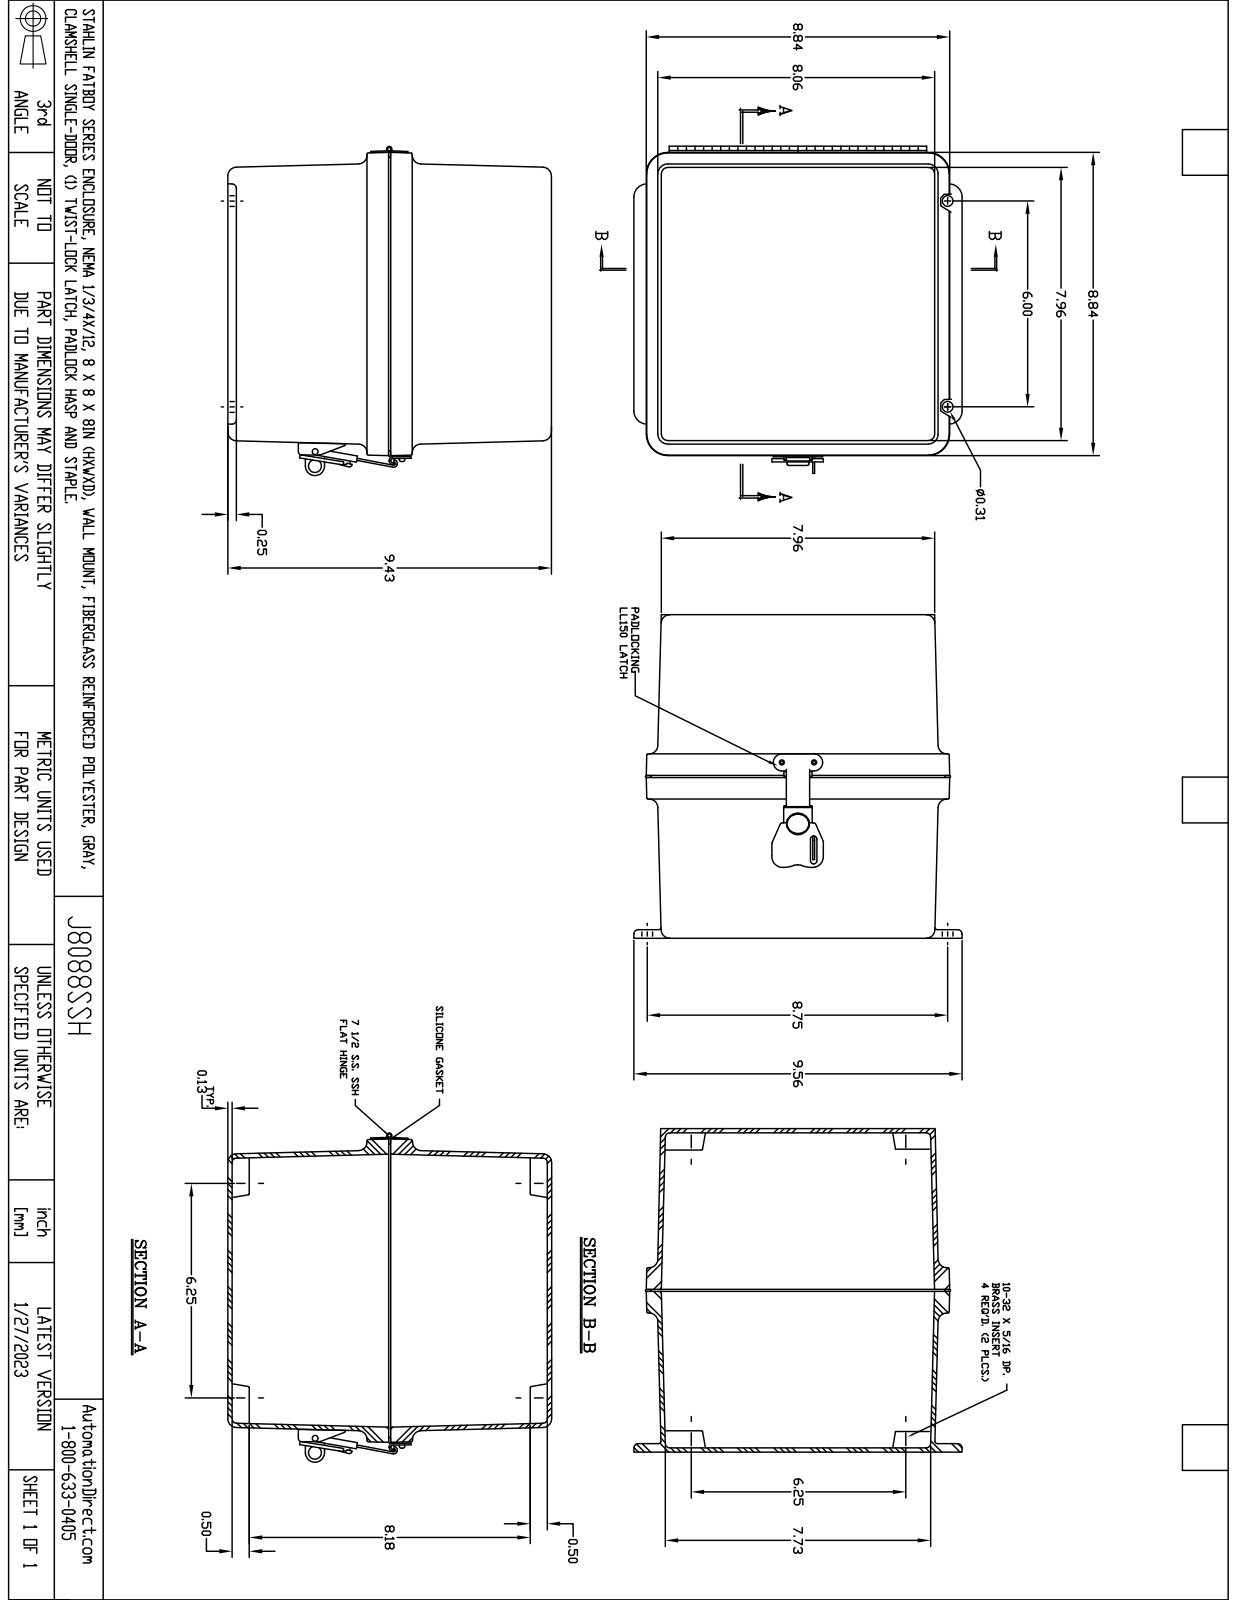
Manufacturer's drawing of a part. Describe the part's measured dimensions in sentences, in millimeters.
The part is named "M8088SSH". Its 3-D file was written by "SolidWorks 2018 (AUTOMOTIVE_DESIGN)". It is 35 solids with 1137 faces: 399 planar, 443 cylindrical and 295 other. Overall it measures 242.9 by 242.7 by 239.5 millimeters. Its volume is 1 172 000 cubic millimeters and its surface area 619 100 square millimeters. Round holes: 11 of diameter 3.9, 10 of diameter 3.6, 7 of diameter 4, 6 of diameter 3.5, 4 of diameter 5.5, 2 of diameter 3.3, 2 of diameter 4.2, 2 of diameter 5, 1 of diameter 2.2, 1 of diameter 2.7, 1 of diameter 3, 1 of diameter 3.5. Round bosses or shafts: 10 of diameter 6.4, 7 of diameter 6.9, 6 of diameter 3.2, 4 of diameter 3.2, 1 of diameter 14.8, 1 of diameter 13.3, 1 of diameter 5.3, 1 of diameter 4.7. Partial cylindrical surfaces (rounded edges, fillets, slot ends): 88 of radius 0.8, 20 of radius 6.4, 12 of radius 3.2, 10 of radius 2, 8 of radius 0.8, 5 of radius 19.1, 4 of radius 0.9, 4 of radius 1. The main face-to-face distances are 3.2, 3.2, 205.4, 202.2, 202.2, 233.1, 239.5, 236.3, 236.3, 205.4. The hole center spacings are 184.1, 158.8, 158.8, 258.2, 184.1, 224.5, 33.7, 76.2.
